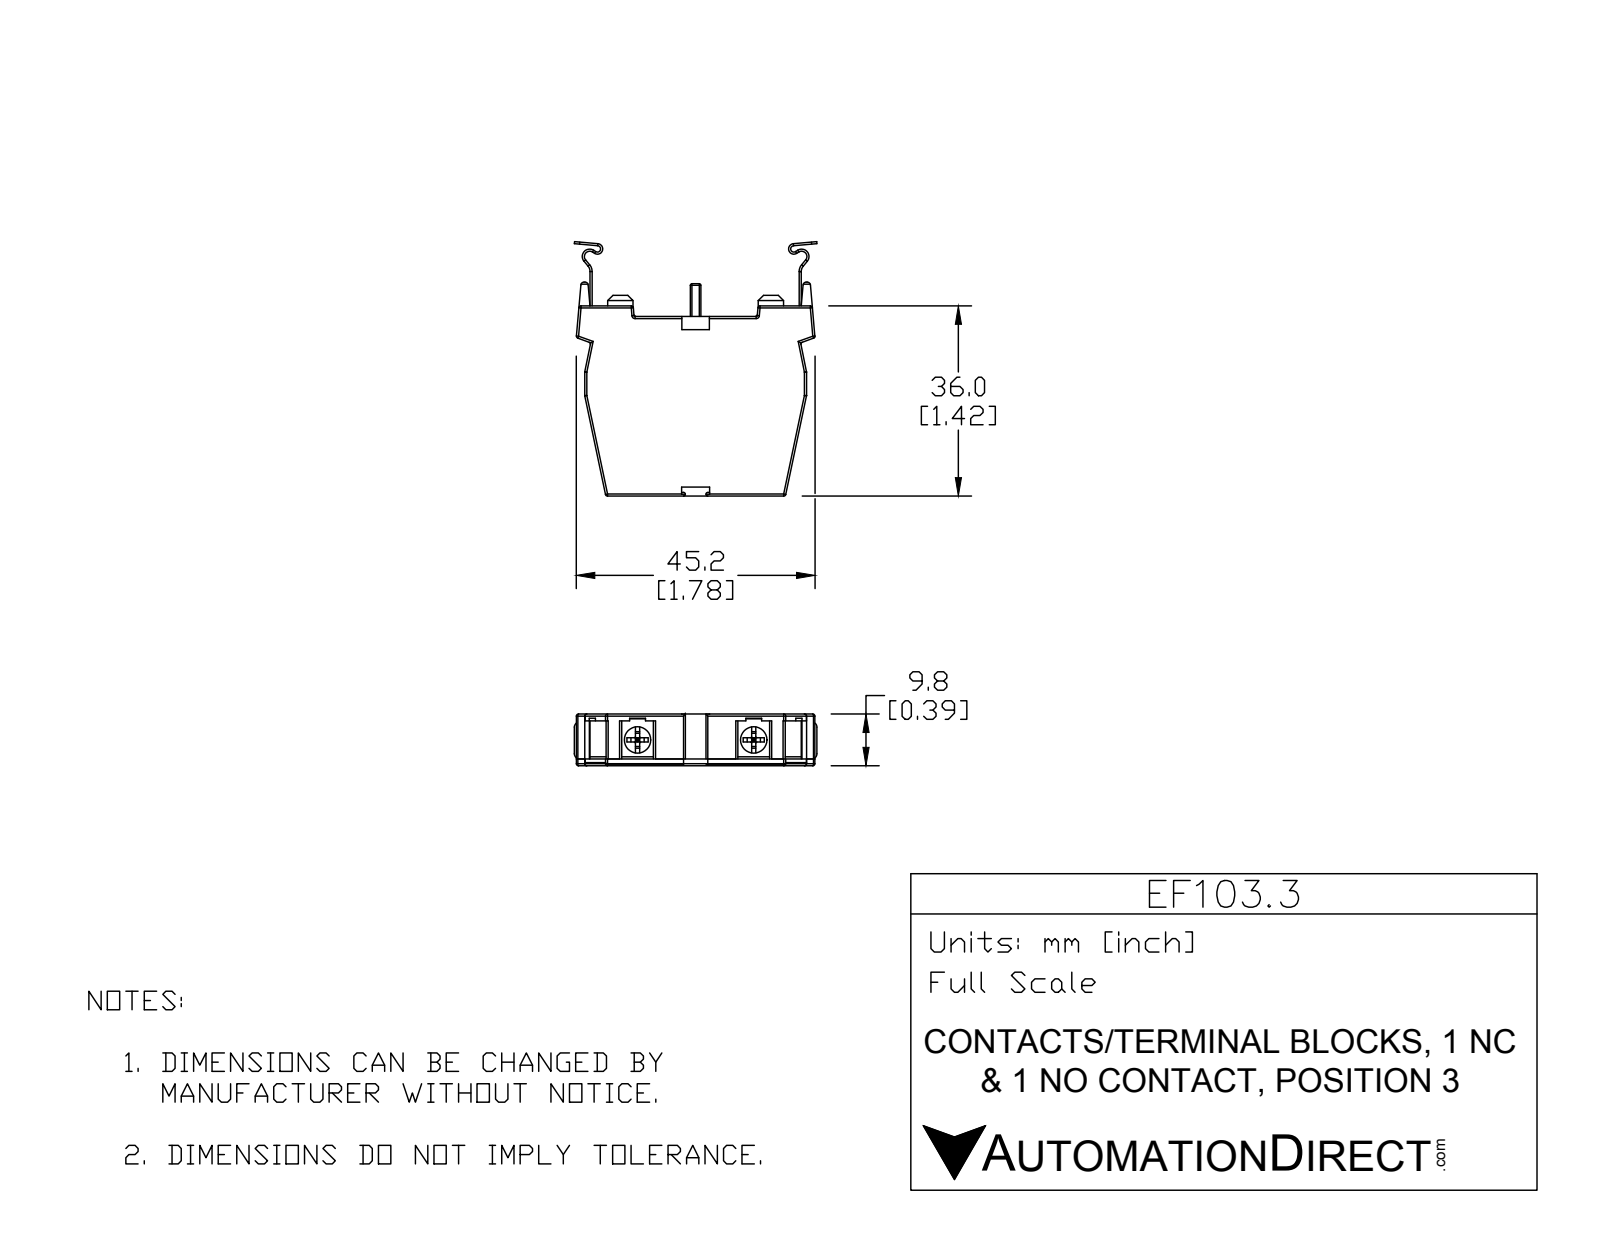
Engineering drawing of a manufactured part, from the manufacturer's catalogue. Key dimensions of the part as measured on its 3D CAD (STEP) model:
Part name (STEP PRODUCT): EF103.3
STEP written by: SolidWorks 2015 (AUTOMOTIVE_DESIGN)
Units: millimetres
Bodies: 7 solids, 299 faces (173 planar, 104 cylindrical, 22 other)
Overall size (bounding box): 48.16 × 46.28 × 9.8
Volume: 12 135 mm³ · Surface area: 6 604 mm²
Round holes (diameter × count): ⌀5 ×4
Round bosses / shafts (diameter × count): ⌀4 ×4, ⌀4.75 ×2
Partial cylindrical surfaces — rounded edges, fillets, slot ends (radius × count): R0.25 ×44, R0.5 ×8, R1 ×6, R0.6 ×4, R0.6 ×2, R1 ×2, R1.4 ×2, R1.6 ×2
Main face-to-face distances: 9.8, 1.4, 8.4, 34, 7, 2, 0.4, 3.18, 37.18, 36
Hole centre spacings: 21.81
